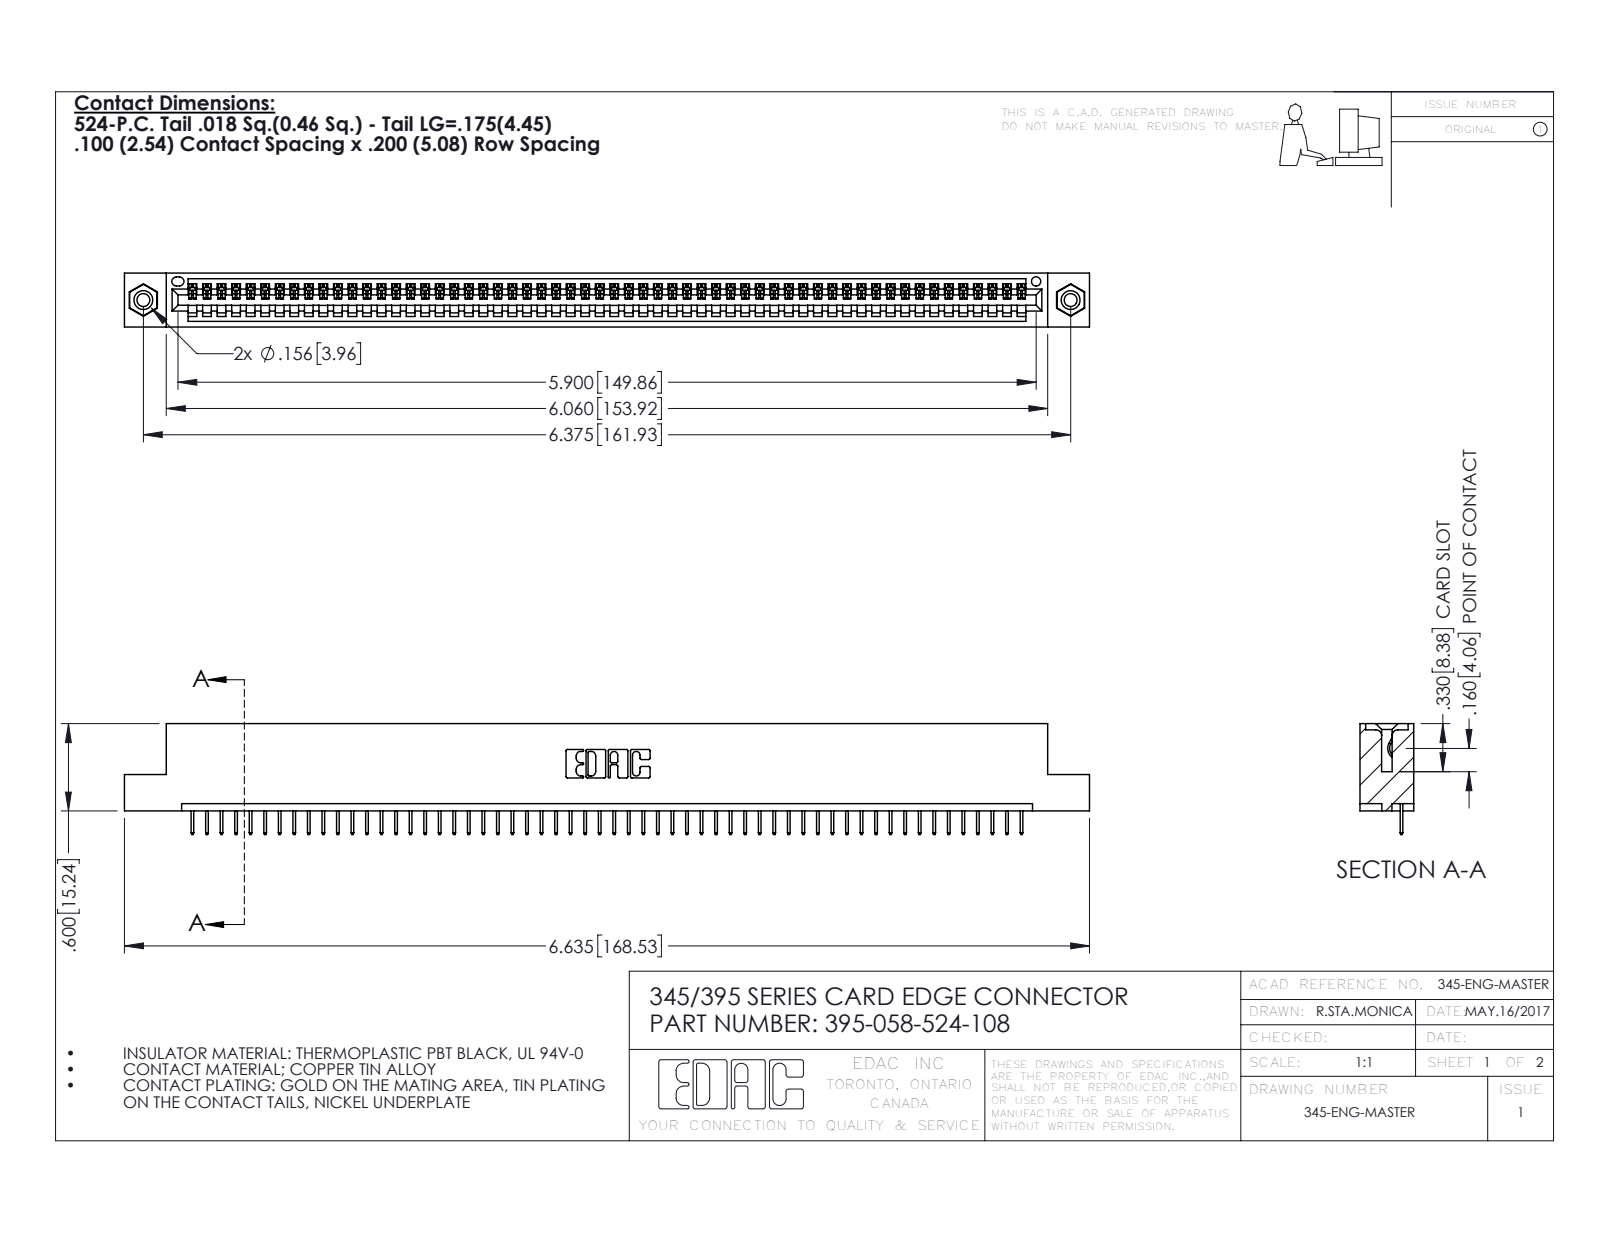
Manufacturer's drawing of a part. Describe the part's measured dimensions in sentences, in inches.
The part is named "395-058-524-108; 345 Part_Flush Mounting Lugs - 0.156 Dia-TI; 345-250-001_345-250-003-102; 345-292-001_345-293-124". Its 3-D file was written by "SolidWorks 2016 (CONFIG_CONTROL_DESIGN)". It is 61 solids with 3782 faces: 2780 planar, 986 cylindrical and 16 other. Overall it measures 6.635 by 0.762 by 0.37 inches. Its volume is 0.97 cubic inches and its surface area 31.99 square inches. Round holes: 2 of diameter 0.089, 2 of diameter 0.125, 2 of diameter 0.156, 1 of diameter 0.064. Round bosses or shafts: 2 of diameter 0.155. Partial cylindrical surfaces (rounded edges, fillets, slot ends): 116 of radius 0.006, 22 of radius 0.01, 6 of radius 0.007, 6 of radius 0.031, 3 of radius 0.026, 2 of radius 0.031, 2 of radius 0.04, 1 of radius 0.014. The main face-to-face distances are 0.072, 0.298, 0.37, 0.2, 0.098, 0.272, 0.025, 0.225, 0.072, 0.149. The hole center spacings are 0.27, 6.139, 6.375.
